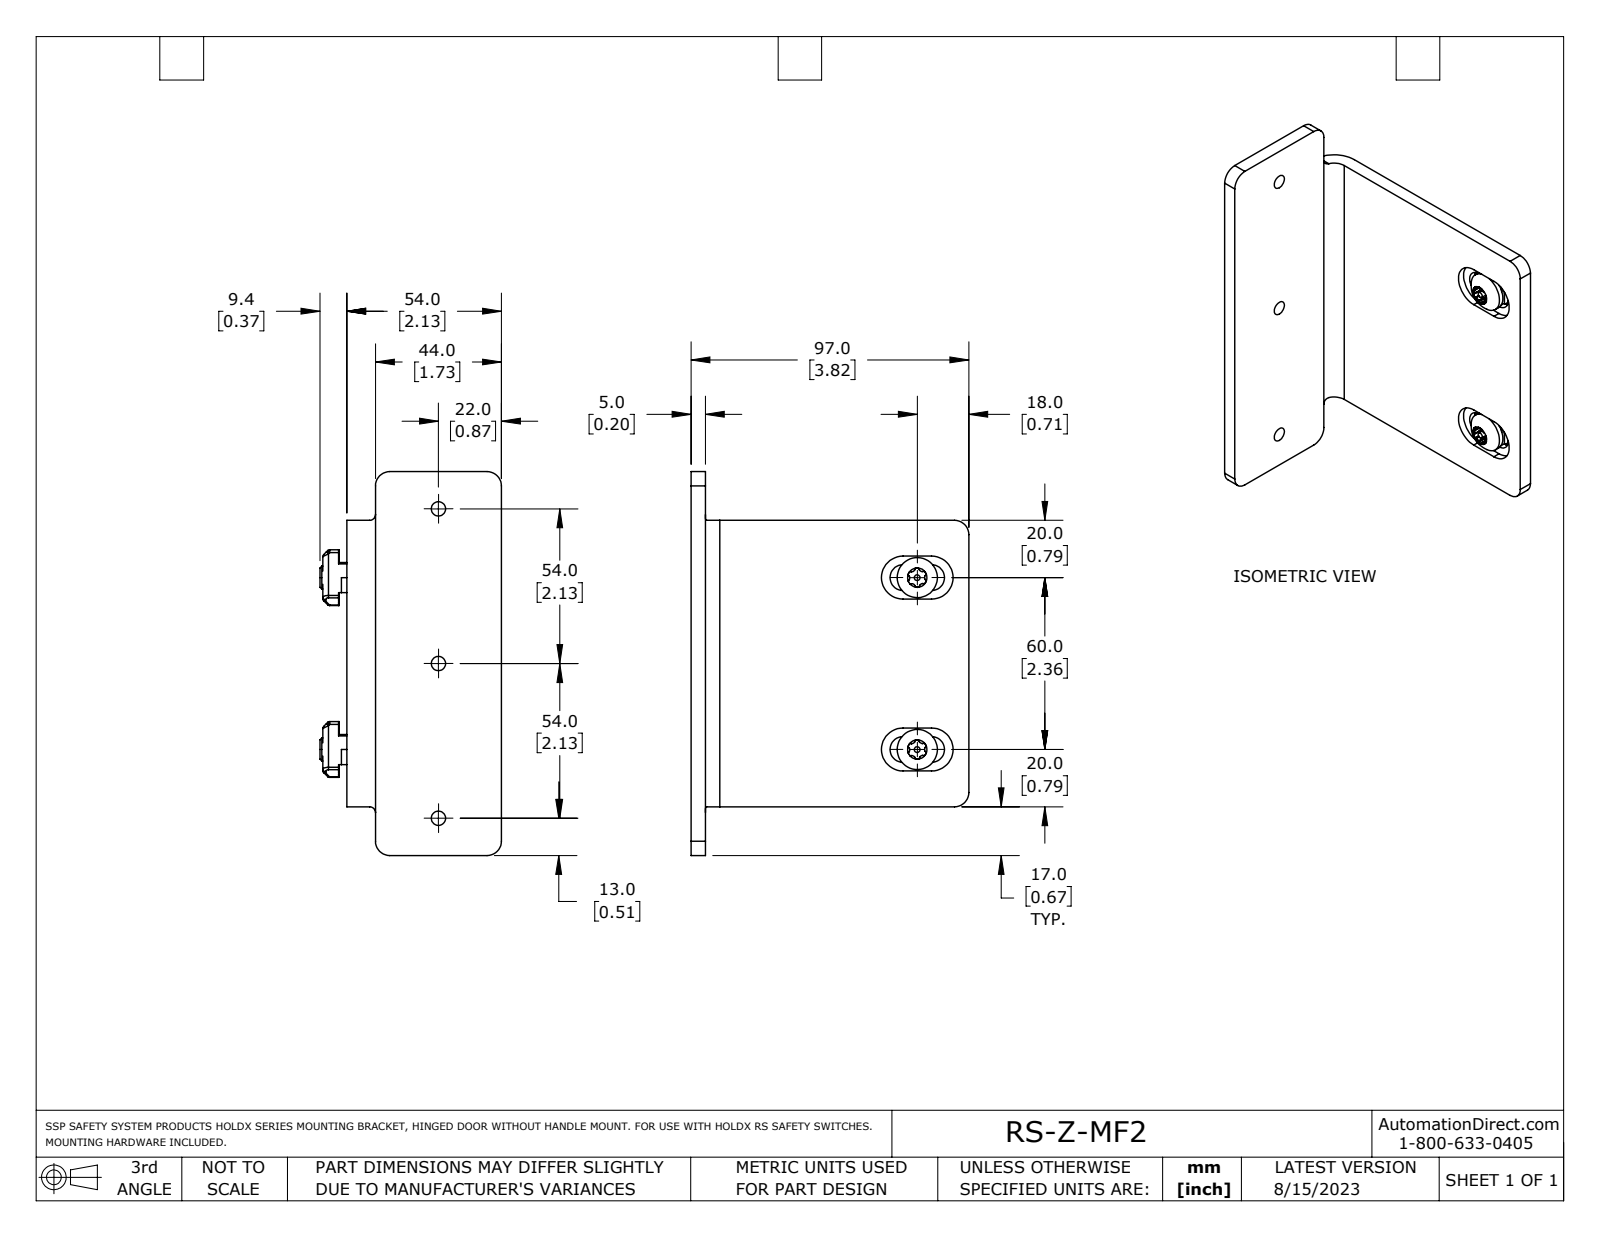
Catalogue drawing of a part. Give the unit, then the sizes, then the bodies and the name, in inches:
Units: inches
Overall size (bounding box): 5.276 × 3.819 × 2.495
Round holes (diameter × count): ⌀0.197 ×3, ⌀0.266 ×2, ⌀0.266 ×2
Round bosses / shafts (diameter × count): ⌀0.551 ×2, ⌀0.315 ×2, ⌀0.079 ×2
Partial cylindrical surfaces — rounded edges, fillets, slot ends (radius × count): R0.011 ×48, R0.039 ×30, R0.056 ×24, R0.197 ×7, R0.079 ×6, R0.02 ×4, R0.177 ×4, R0.295 ×4
Main face-to-face distances: 0.197, 0.098, 2.126, 1.929, 3.937, 3.819, 3.622, 2.028, 0.669, 4.606
Hole centre spacings: 2.126, 2.362, 4.252
Volume: 4.888 in³ · Surface area: 58.19 in²
Bodies: 5 solids, 293 faces (118 planar, 149 cylindrical, 26 other)
Part name (STEP PRODUCT): RS-Z-MF2
STEP written by: SolidWorks 2021 (AUTOMOTIVE_DESIGN)
